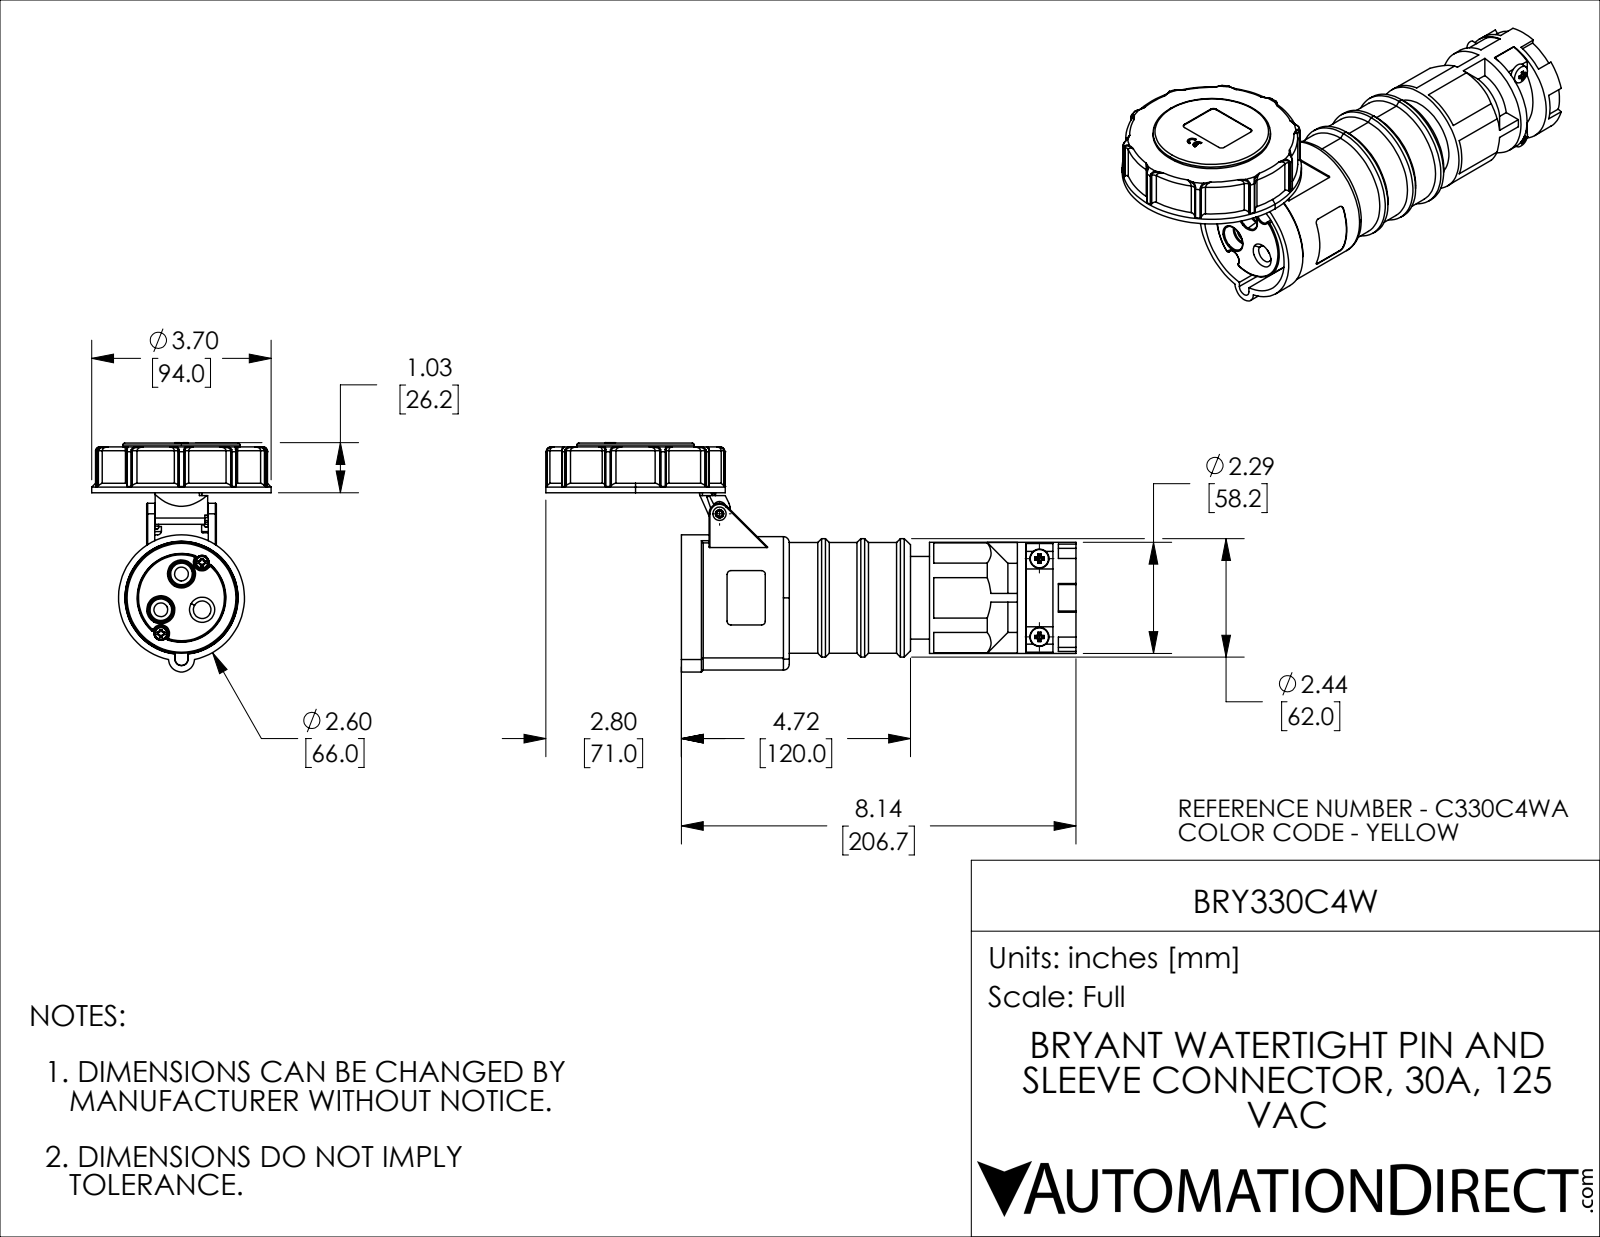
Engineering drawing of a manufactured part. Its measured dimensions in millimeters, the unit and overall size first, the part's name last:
Units: millimetres
Overall size (bounding box): 277.7 × 120.05 × 94
Round holes (diameter × count): ⌀5 ×2, ⌀7.2 ×2, ⌀3 ×1, ⌀4.3 ×1, ⌀7 ×1, ⌀9.2 ×1, ⌀29.5 ×1, ⌀49.04 ×1, ⌀84 ×1
Round bosses / shafts (diameter × count): ⌀94 ×1, ⌀66 ×1, ⌀64 ×1, ⌀62 ×1, ⌀61.5 ×1, ⌀58.2 ×1, ⌀58 ×1, ⌀43.33 ×1
Partial cylindrical surfaces — rounded edges, fillets, slot ends (radius × count): R0.5 ×25, R2.5 ×24, R2 ×9, R0.75 ×5, R1.25 ×4, R1 ×3, R1.75 ×2, R3.4 ×2
Main face-to-face distances: 4.5, 21, 64.7, 10, 18.7, 2, 46, 23, 54.2, 127.5
Hole centre spacings: 12.5, 21.65, 21.66, 41, 169.24, 179.58
Volume: 578 977 mm³ · Surface area: 115 441 mm²
Bodies: 7 solids, 831 faces (281 planar, 265 cylindrical, 285 other)
Part name (STEP PRODUCT): BRY330C4W
STEP written by: SolidWorks 2021 (CONFIG_CONTROL_DESIGN)
